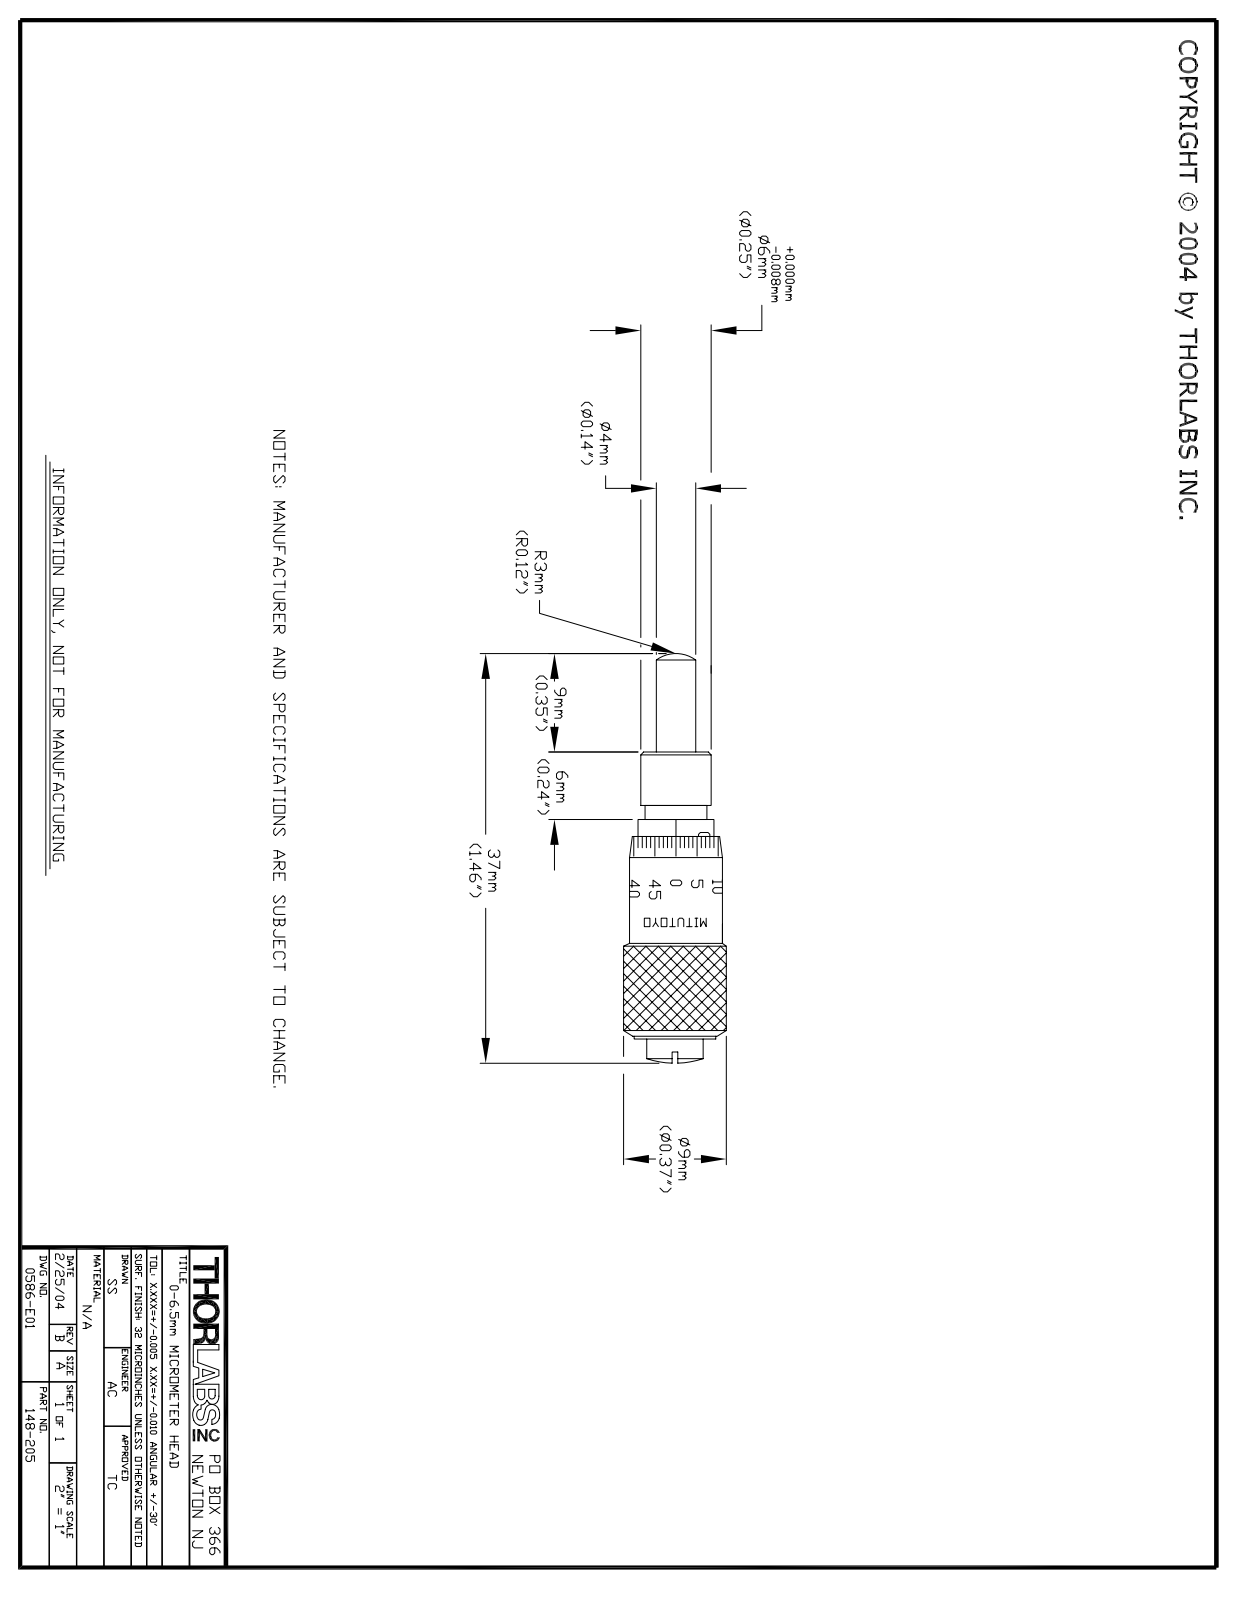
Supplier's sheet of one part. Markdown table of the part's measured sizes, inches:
| quantity | value |
| --- | --- |
| part name | 0586-E0W |
| STEP written by | SolidWorks 2007 (AUTOMOTIVE_DESIGN) |
| units | inches |
| bodies | 0 solids, 39 faces (9 planar, 16 cylindrical, 14 other) |
| overall size | 1.456 × 0.365 × 0.365 |
| round bosses / shafts (diameter × count) | 0.365 × 1, 0.337 × 1, 0.29 × 1, 0.277 × 1, 0.257 × 1, 0.227 × 1, 0.2 × 1, 0.147 × 1 |
| main face-to-face distances | 1.02, 0.24, 0.78, 0.3, 0.06, 0.72, 0.19, 0.05, 0.11, 0.83 |
